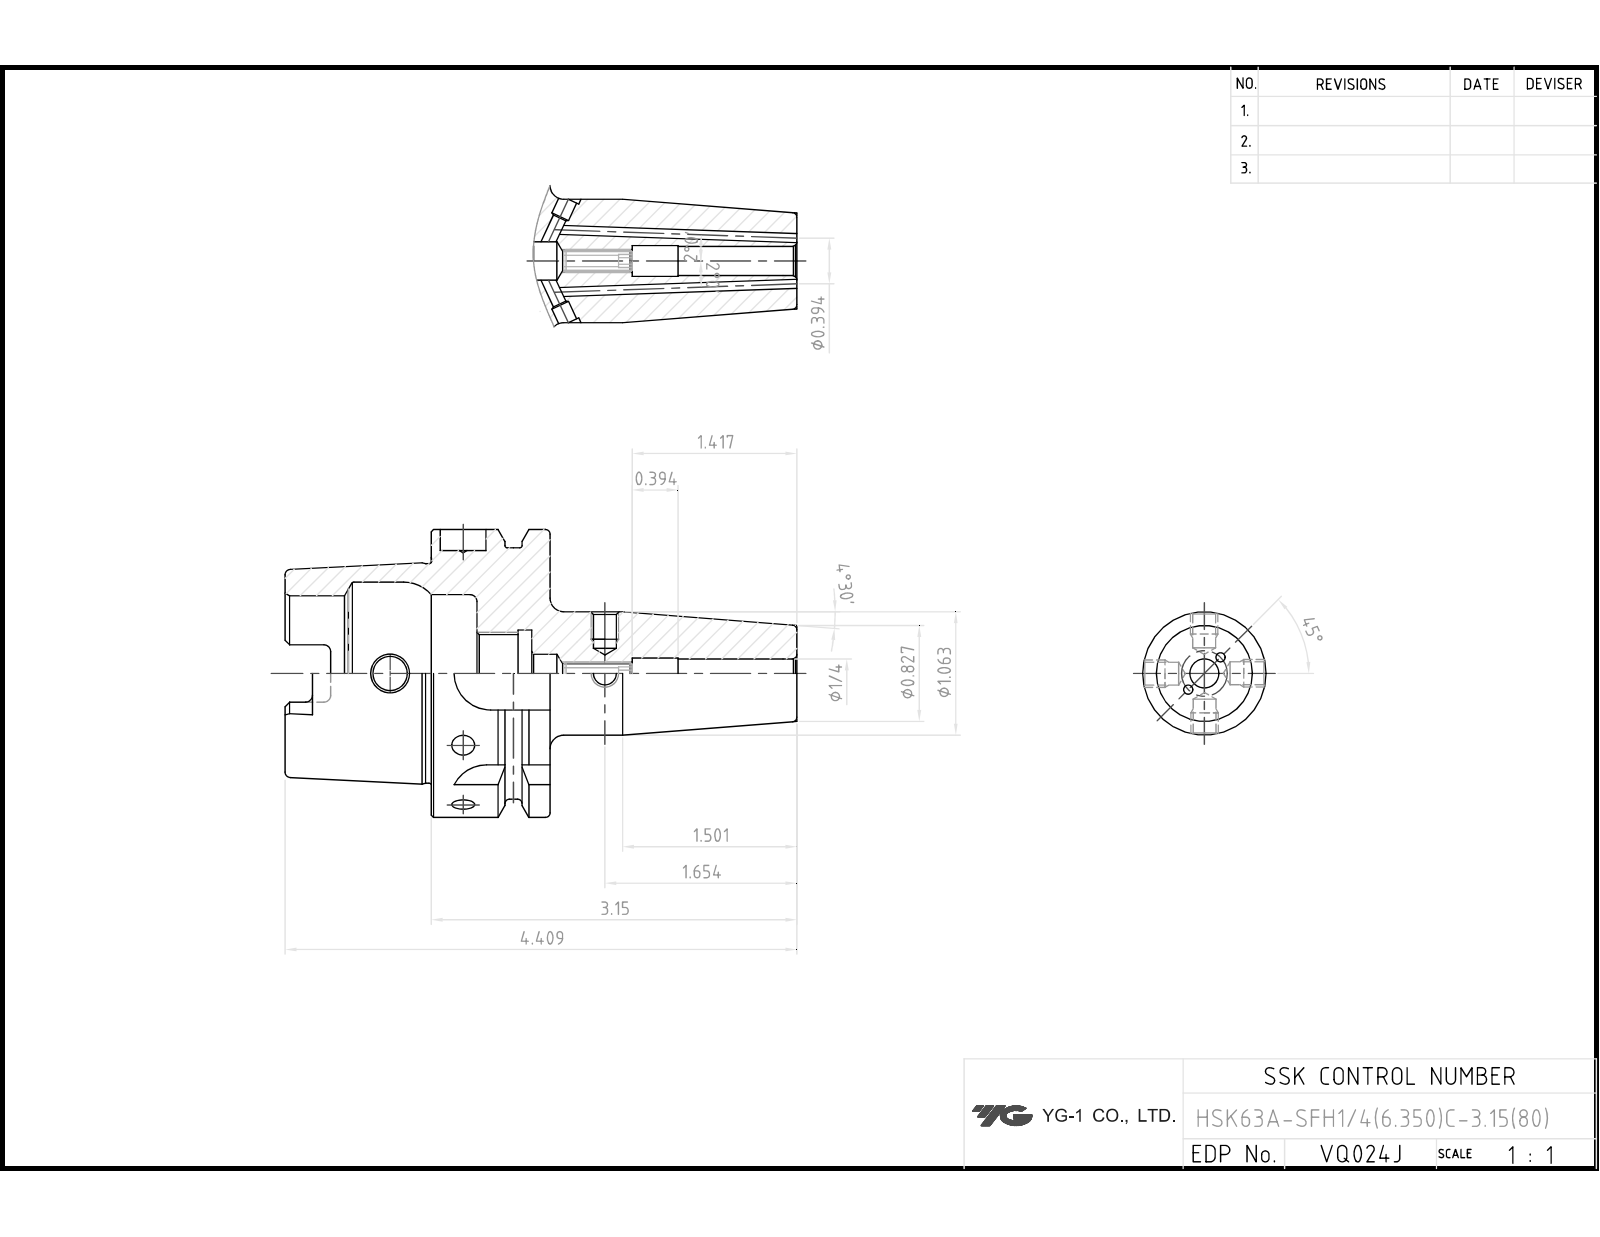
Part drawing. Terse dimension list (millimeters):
name: VQ024J-HSK63A-SFH0_25C-3_15
written by: CREO PARAMETRIC BY PTC INC, 2018100 (CONFIG_CONTROL_DESIGN)
unit: mm
bodies: 1 solid, 208 faces (65 planar, 73 cylindrical, 70 other)
size: 112 × 63 × 63
volume: 105 439 mm³; area: 29 585 mm²
holes: 3× ⌀5, 2× ⌀2, 2× ⌀6, 1× ⌀4.2, 1× ⌀6.35, 1× ⌀6.75, 1× ⌀7.5, 1× ⌀8.4, 1× ⌀10, 1× ⌀17, 1× ⌀18, 1× ⌀19
bosses: 1× ⌀63, 1× ⌀55, 1× ⌀48.04, 1× ⌀27
rounds: 6× R1.5, 4× R2.88, 4× R8
face distances: 26, 10, 58, 16, 54, 32, 6.12, 9.88, 42, 4
hole spacings: 31, 47
